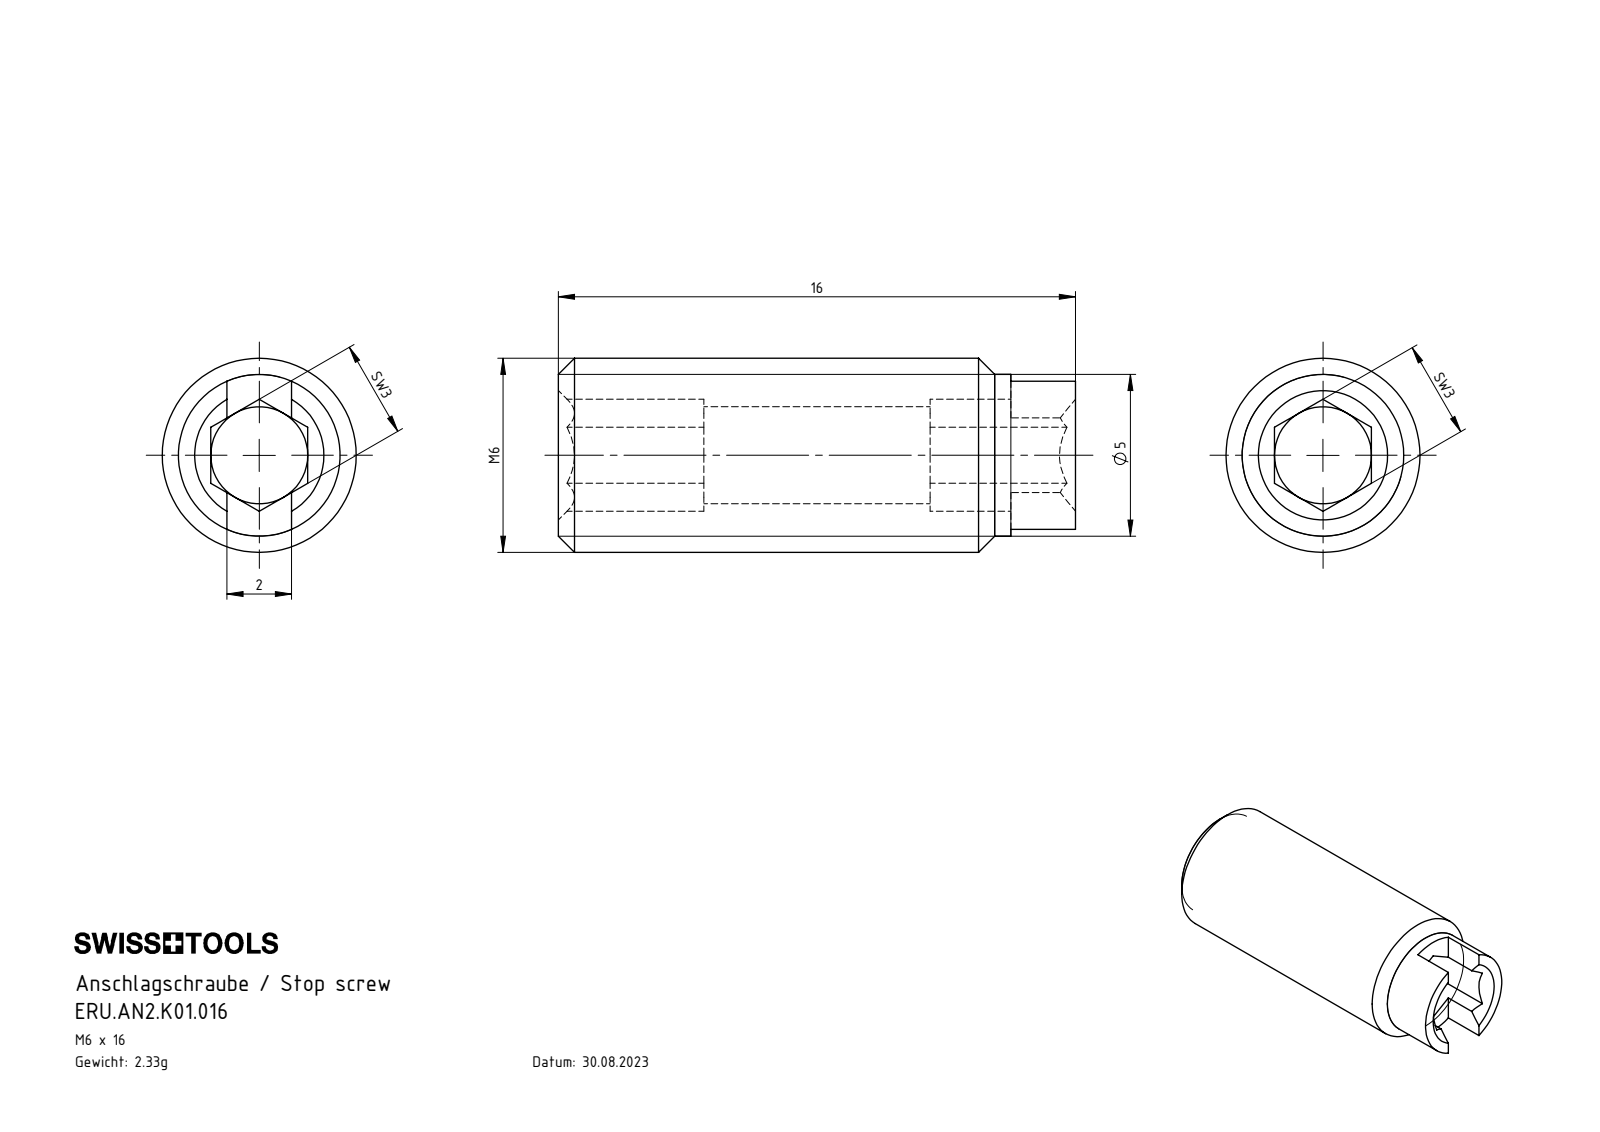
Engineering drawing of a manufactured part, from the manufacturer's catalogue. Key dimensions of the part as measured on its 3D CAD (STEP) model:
Part name (STEP PRODUCT): ERU.AN2.K01.016
STEP written by: SolidWorks 2017 (AUTOMOTIVE_DESIGN)
Units: millimetres
Bodies: 1 solid, 48 faces (33 planar, 6 cylindrical, 9 other)
Overall size (bounding box): 16 × 6 × 6
Volume: 297 mm³ · Surface area: 471 mm²
Round holes (diameter × count): ⌀3 ×1
Round bosses / shafts (diameter × count): ⌀6 ×1, ⌀5 ×1
Main face-to-face distances: 3, 2.5, 0.5, 2, 16, 14, 4.5, 11.5, 9.5, 7
